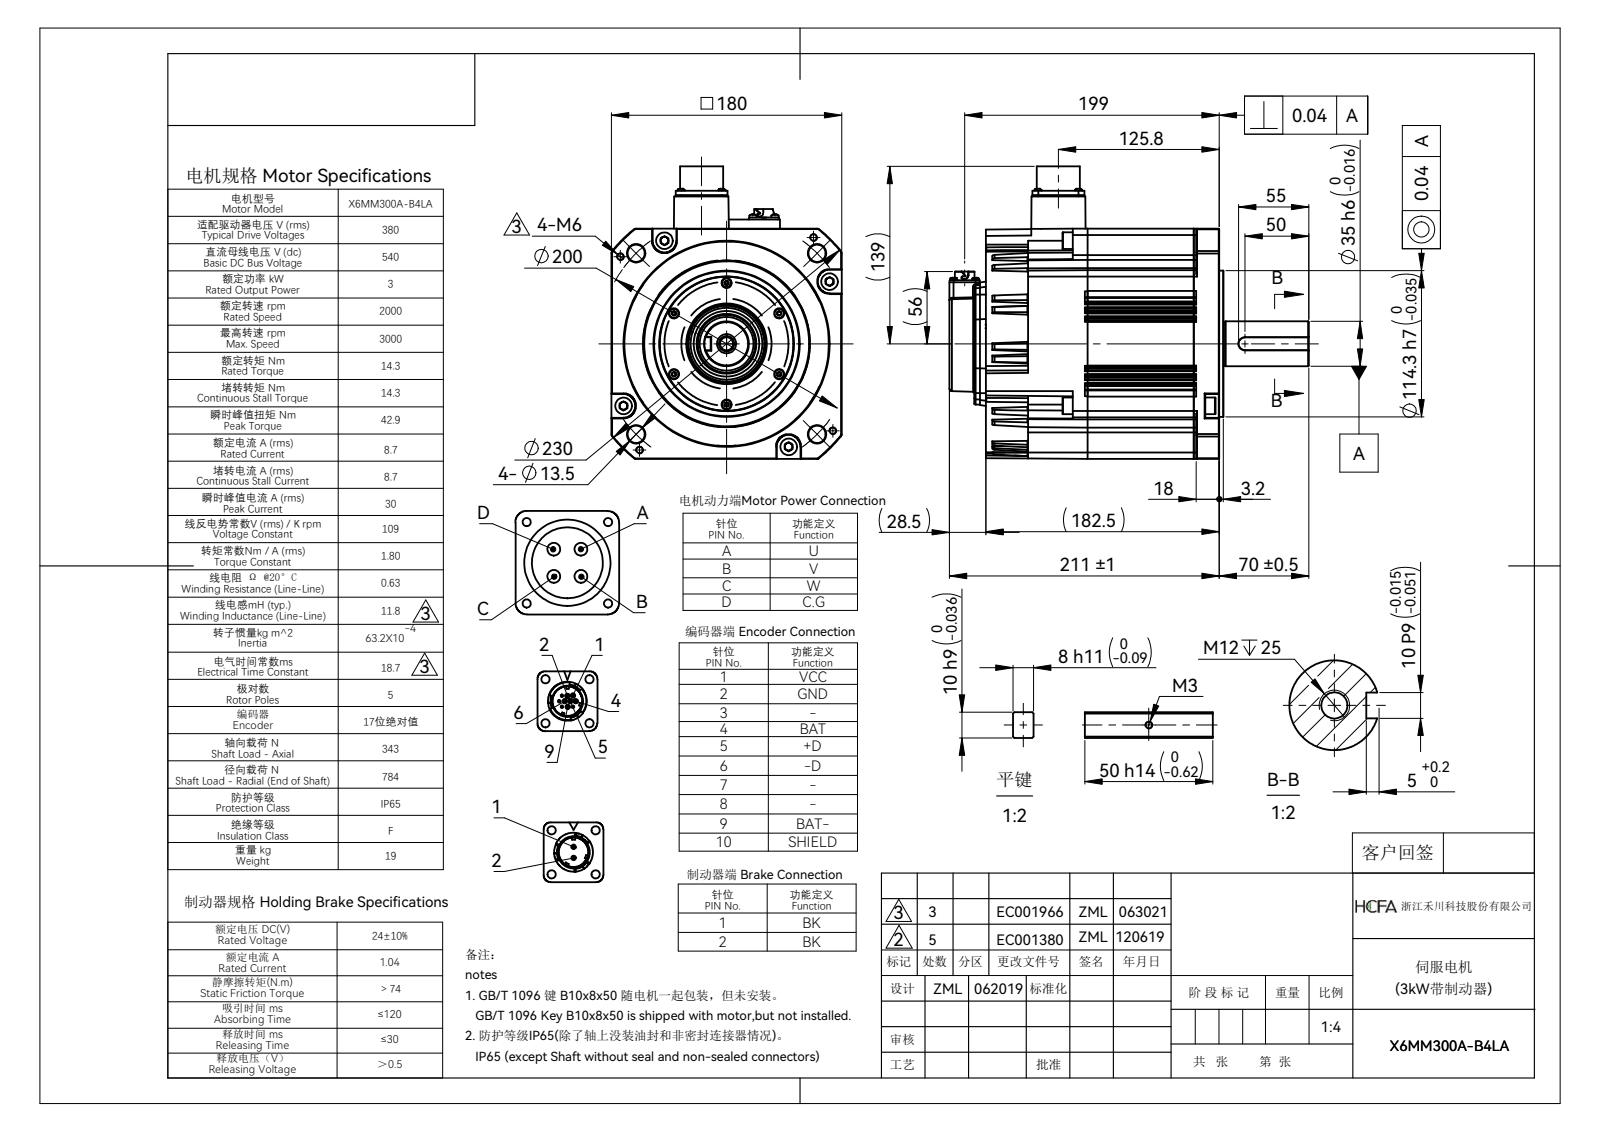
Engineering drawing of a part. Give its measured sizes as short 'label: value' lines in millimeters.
name: SV-X2MM300A-B4LA
written by: SolidWorks 2016 (CONFIG_CONTROL_DESIGN)
unit: mm
bodies: 1 solid, 2181 faces (858 planar, 709 cylindrical, 614 other)
size: 281 × 228.55 × 180
volume: 5 259 000 mm³; area: 255 570 mm²
holes: 4× ⌀13.5, 2× ⌀11.6, 1× ⌀10.2, 1× ⌀11.75, 1× ⌀11.8, 1× ⌀27.7, 1× ⌀32.5
bosses: 10× ⌀1, 8× ⌀5.7, 4× ⌀13, 4× ⌀5.6, 4× ⌀5, 4× ⌀3, 2× ⌀15.2, 2× ⌀0.75
rounds: 105× R0.5, 48× R1, 29× R5, 18× R2, 16× R0.55, 8× R0.2, 8× R3, 4× R2.8
face distances: 180, 32.5, 182.5, 147.5, 185.7, 3.2, 115, 4, 178.5, 7.2
hole spacings: 100, 141.42, 200, 48.75, 75.81, 78.87
